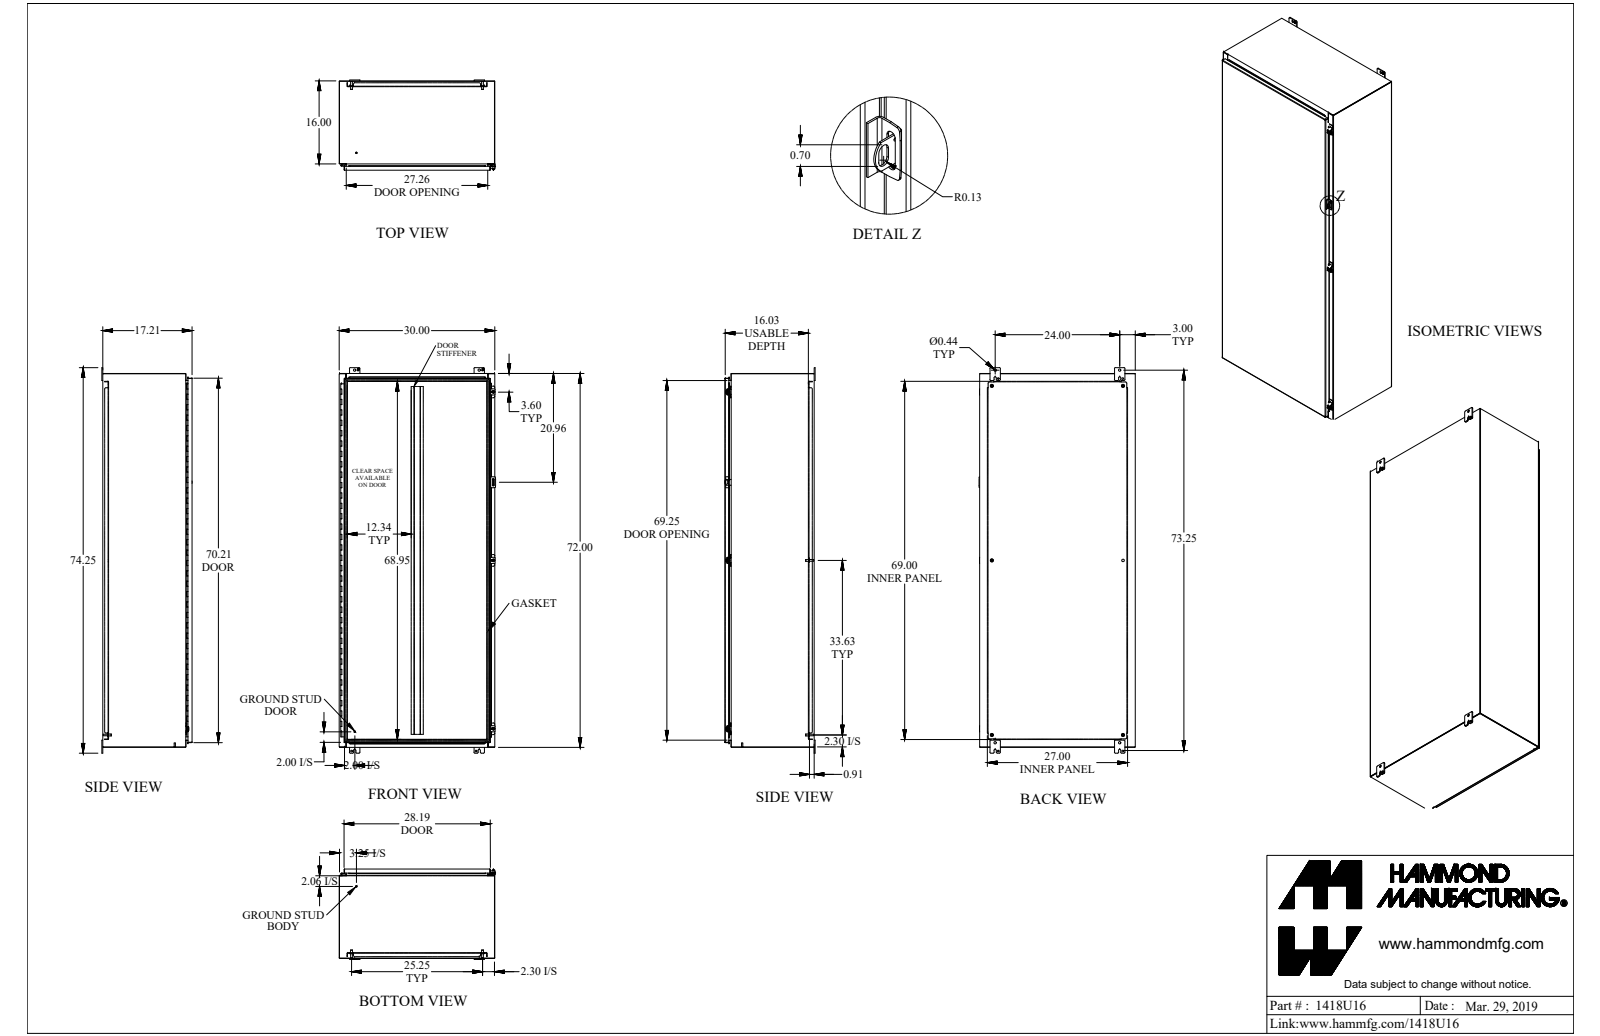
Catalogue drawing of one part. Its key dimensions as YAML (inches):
part_name: "1418U16_Default"
step_written_by: "SolidWorks 2019 (CONFIG_CONTROL_DESIGN)"
units: inches
bodies: {solids: 34, faces: 1662, planar: 945, cylindrical: 647, other: 70}
overall_size: [74.25, 30.094, 17.437]
volume: 838.2
surface_area: 21776
round_holes:
  - {diameter: 0.304, count: 17}
  - {diameter: 0.5, count: 6}
  - {diameter: 0.313, count: 4}
  - {diameter: 0.437, count: 4}
  - {diameter: 0.213, count: 3}
  - {diameter: 0.125, count: 1}
  - {diameter: 0.187, count: 1}
round_bosses_or_shafts:
  - {diameter: 0.65, count: 8}
  - {diameter: 0.375, count: 8}
  - {diameter: 0.33, count: 8}
  - {diameter: 0.39, count: 3}
  - {diameter: 0.313, count: 2}
  - {diameter: 0.25, count: 2}
  - {diameter: 0.287, count: 1}
partial_cylinders:
  - {radius: 0.188, count: 40}
  - {radius: 0.048, count: 25}
  - {radius: 0.25, count: 20}
  - {radius: 0.143, count: 19}
  - {radius: 0.036, count: 16}
  - {radius: 0.108, count: 16}
  - {radius: 0.116, count: 16}
  - {radius: 0.125, count: 8}
face_to_face_distances: [0.072, 17.113, 17.041, 29.928, 17.185, 0.095, 16.176, 16.104, 0.937, 1.009]
hole_center_spacings: [4, 8, 24, 12, 16, 20, 28, 32]
